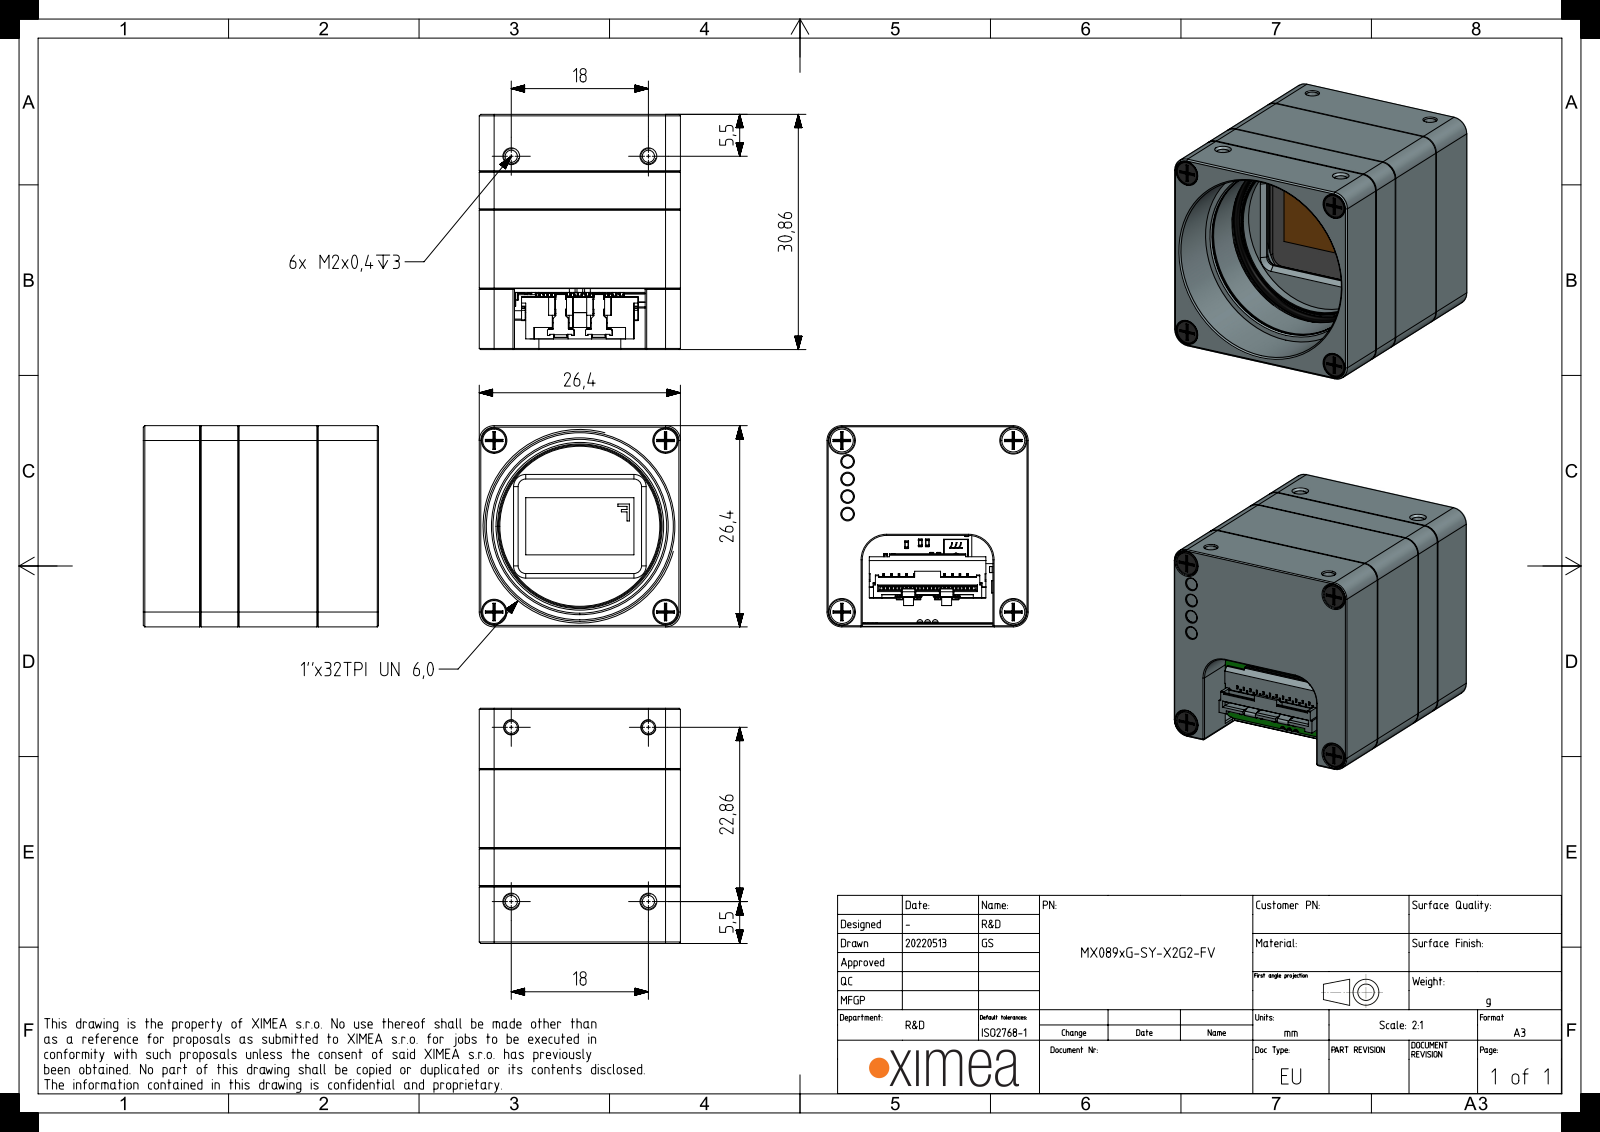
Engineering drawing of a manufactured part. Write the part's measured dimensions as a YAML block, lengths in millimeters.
part_name: "SROB-M2x10-CUST; MECH-MX-THERMAL-PAD-10X10; MECH-LIGHTPIPE-1.63x4.14; MX-X2G2-MAIN-FV-PCA (+8 more)"
step_written_by: "SIEMENS PLM Software NX 1907 (AUTOMOTIVE_DESIGN)"
units: millimeters
bodies: {solids: 32, faces: 7538, planar: 5247, cylindrical: 2016, other: 275}
overall_size: [30.9, 26.4, 26.4]
volume: 10400
surface_area: 17910
round_holes:
  - {diameter: 1.6, count: 12}
  - {diameter: 0.9, count: 4}
  - {diameter: 2, count: 4}
  - {diameter: 2.1, count: 4}
  - {diameter: 3, count: 4}
  - {diameter: 3.2, count: 4}
  - {diameter: 3.4, count: 4}
  - {diameter: 1.3, count: 2}
  - {diameter: 1.7, count: 2}
  - {diameter: 21, count: 1}
  - {diameter: 22.8, count: 1}
  - {diameter: 24.4, count: 1}
round_bosses_or_shafts:
  - {diameter: 1.9, count: 4}
  - {diameter: 1.6, count: 4}
  - {diameter: 0.8, count: 4}
  - {diameter: 3, count: 2}
  - {diameter: 1.6, count: 2}
  - {diameter: 25, count: 1}
  - {diameter: 21.6, count: 1}
partial_cylinders:
  - {radius: 0.3, count: 16}
  - {radius: 1.5, count: 15}
  - {radius: 0.2, count: 14}
  - {radius: 1, count: 14}
  - {radius: 0.1, count: 12}
  - {radius: 0.4, count: 12}
  - {radius: 0.3, count: 8}
  - {radius: 0.5, count: 8}
face_to_face_distances: [1, 26.4, 3.6, 11.5, 6.9, 2.5, 4.6, 10.5, 10.4, 6.8]
hole_center_spacings: [15.9, 22.5, 2.3, 3.8, 4.6, 13.5, 18, 18.7]
